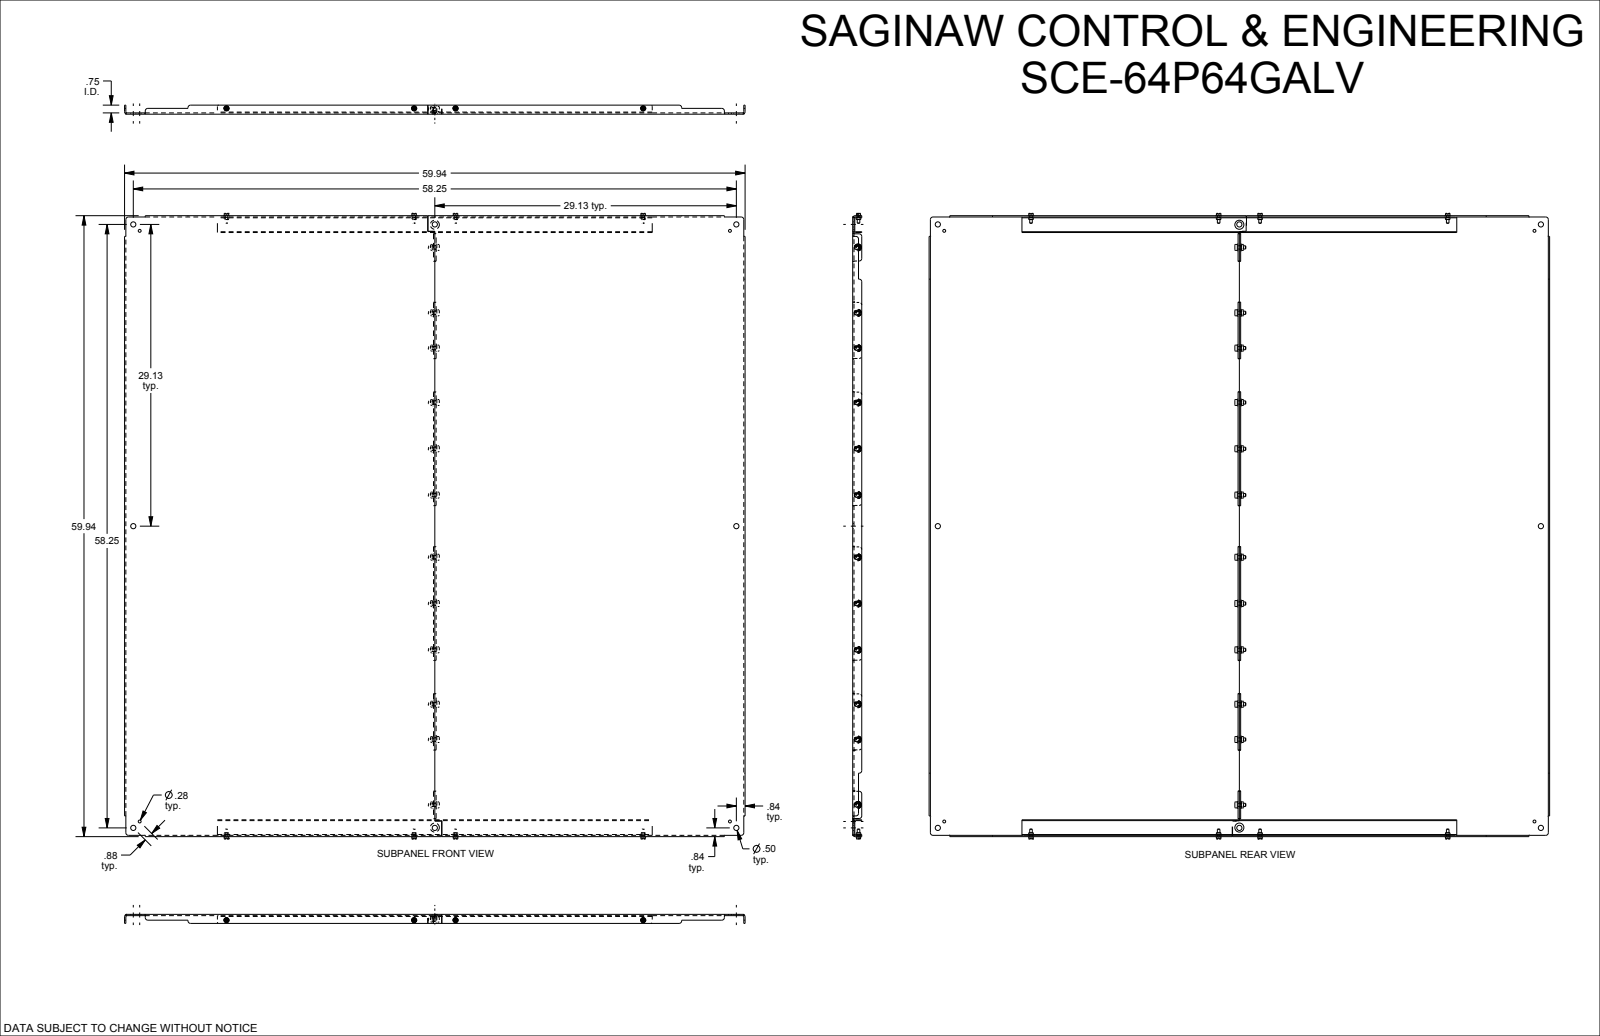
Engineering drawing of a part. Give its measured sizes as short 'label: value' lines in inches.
name: SCE-64P64GALV
written by: SolidWorks 2019 (CONFIG_CONTROL_DESIGN)
unit: in
bodies: 44 solids, 1922 faces (528 planar, 478 cylindrical, 916 other)
size: 60.386 × 59.938 × 0.875
volume: 492.7 in³; area: 8 132 in²
holes: 12× ⌀0.312, 12× ⌀0.375, 8× ⌀0.5, 4× ⌀0.25, 4× ⌀0.308, 4× ⌀0.344, 3× ⌀0.281, 2× ⌀0.875, 1× ⌀0.28
bosses: 12× ⌀0.31, 4× ⌀0.5, 4× ⌀0.44, 4× ⌀0.343, 4× ⌀0.248
rounds: 200× R0.01, 24× R0.25, 16× R0.06, 8× R0.172, 6× R0.112, 6× R0.237, 4× R0.08, 4× R0.158
face distances: 0.125, 0.125, 0.078, 0.203, 29.844, 1.422, 58.187, 59.813, 0.078, 59.687
hole spacings: 29.125, 28.513, 65.125, 57.634, 64.296, 0.875, 28.512, 29.125
